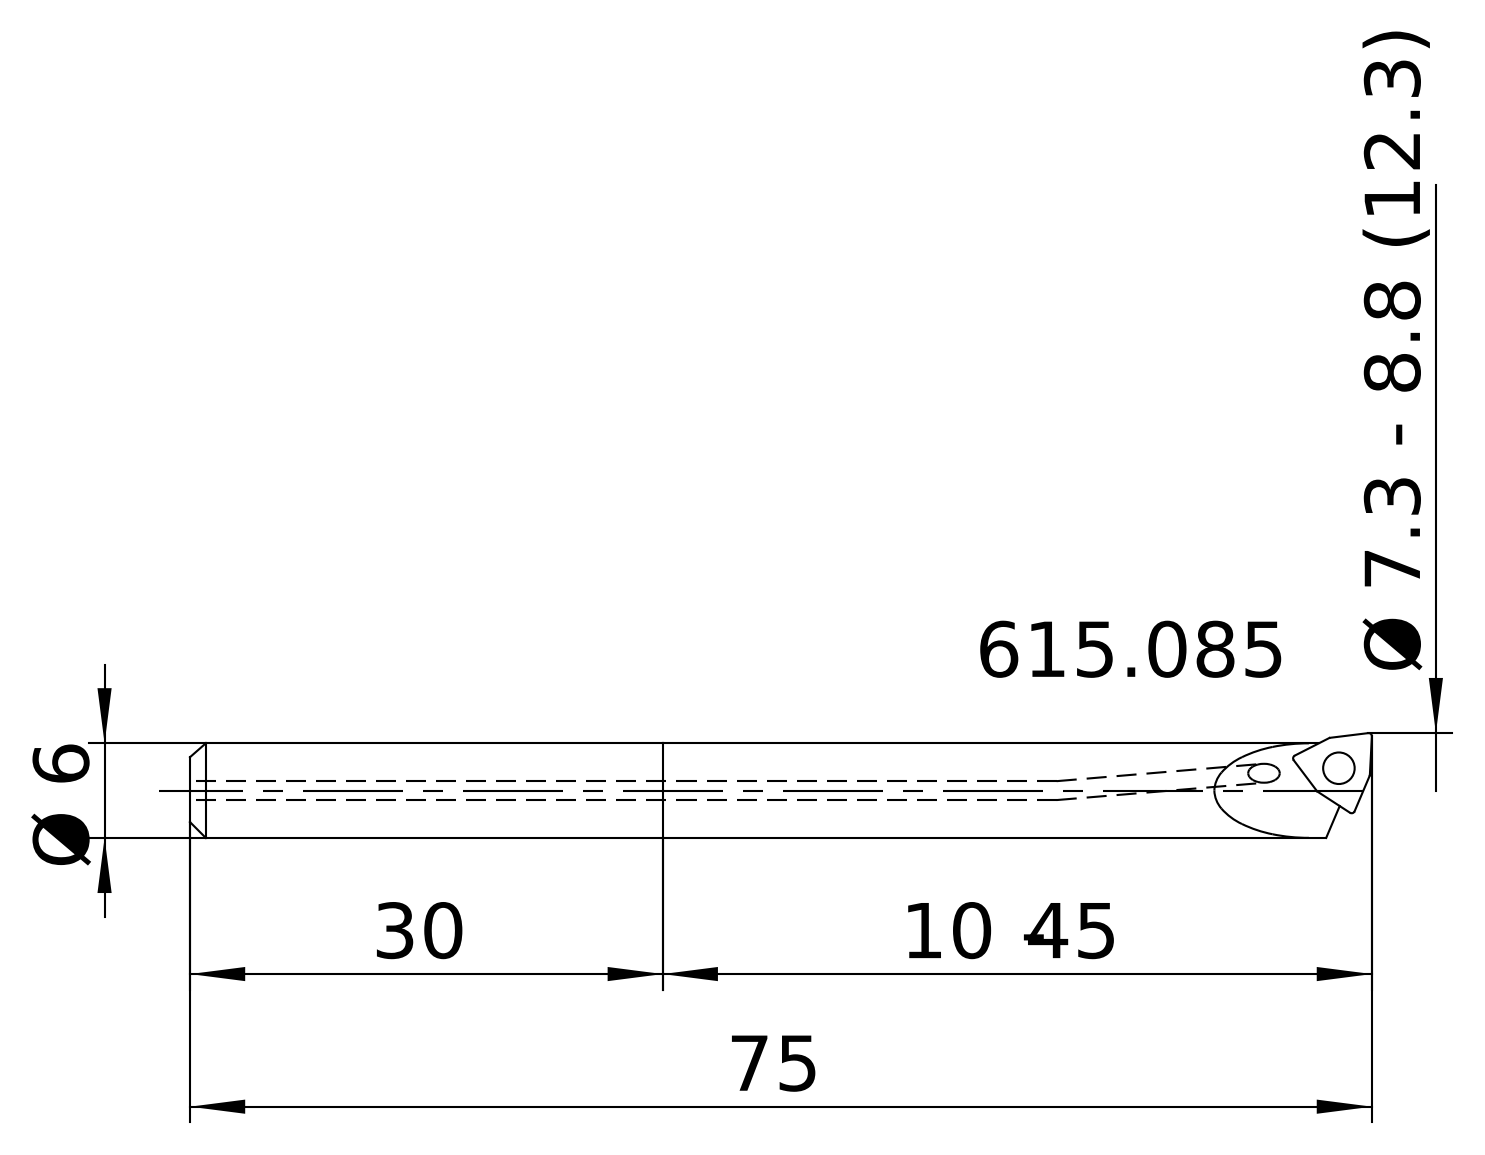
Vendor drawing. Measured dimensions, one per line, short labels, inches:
written by: ACIS (automotive_design)
unit: in
bodies: 4 solids, 98 faces (29 planar, 37 cylindrical, 32 other)
size: 2.953 × 0.255 × 0.236
volume: 0.117 in³; area: 2.933 in²
holes: 2× ⌀0.059, 1× ⌀0.063, 1× ⌀0.087, 1× ⌀0.094, 1× ⌀0.118
bosses: 1× ⌀0.236, 1× ⌀0.106, 1× ⌀0.079
rounds: 6× R0.006, 6× R0.012, 1× R0.083
face distances: 0.063, 0.055, 0.075, 0.02, 0.013, 0.067, 0.122, 0.129, 0.142, 0.111
